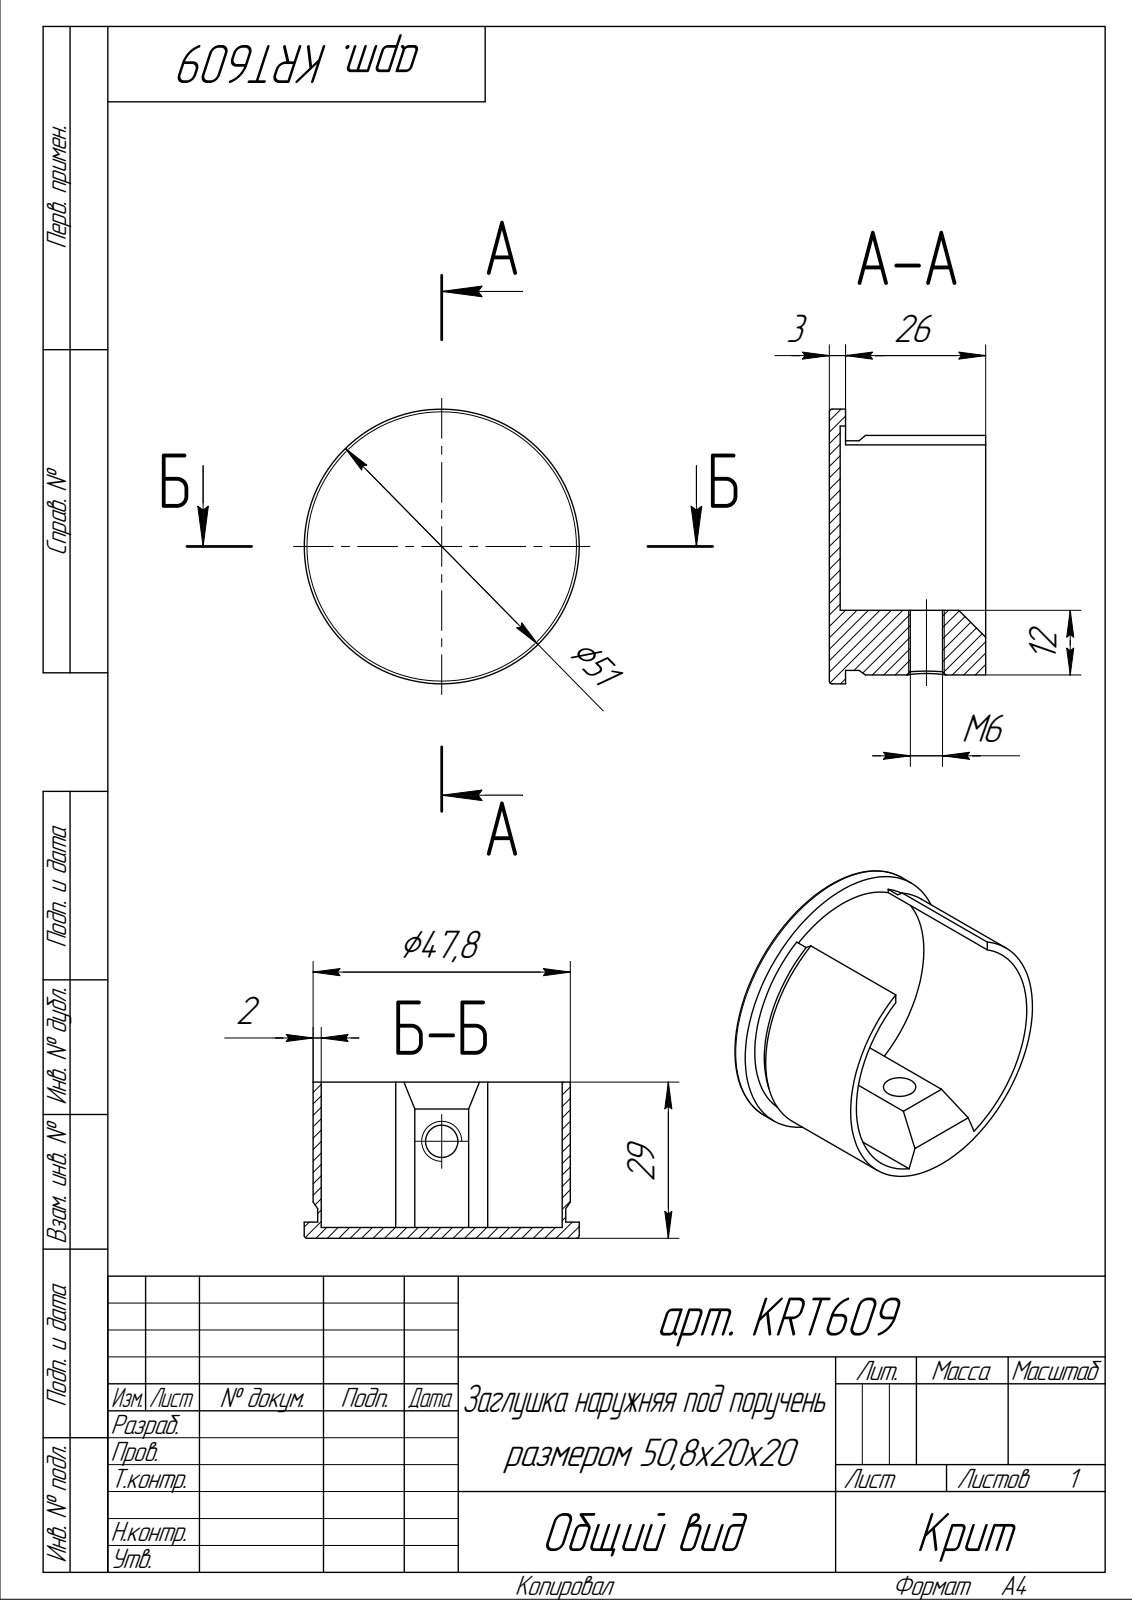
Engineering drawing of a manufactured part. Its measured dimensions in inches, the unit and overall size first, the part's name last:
Units: inches
Overall size (bounding box): 2.008 × 2.008 × 1.142
Round holes (diameter × count): ⌀0.236 ×1, ⌀1.76 ×1
Round bosses / shafts (diameter × count): ⌀2.008 ×1, ⌀1.878 ×1, ⌀1.811 ×1
Main face-to-face distances: 0.079, 0.118, 0.039, 1.142, 1.063, 1.024, 0.945
Volume: 0.742 in³ · Surface area: 17.87 in²
Bodies: 1 solid, 18 faces (10 planar, 5 cylindrical, 3 other)
Part name (STEP PRODUCT): арт. KRT609 Заглушка наружняя под поручень размером 50,8х20х20
STEP written by: ASCON Math Kernel (AUTOMOTIVE_DESIGN)
